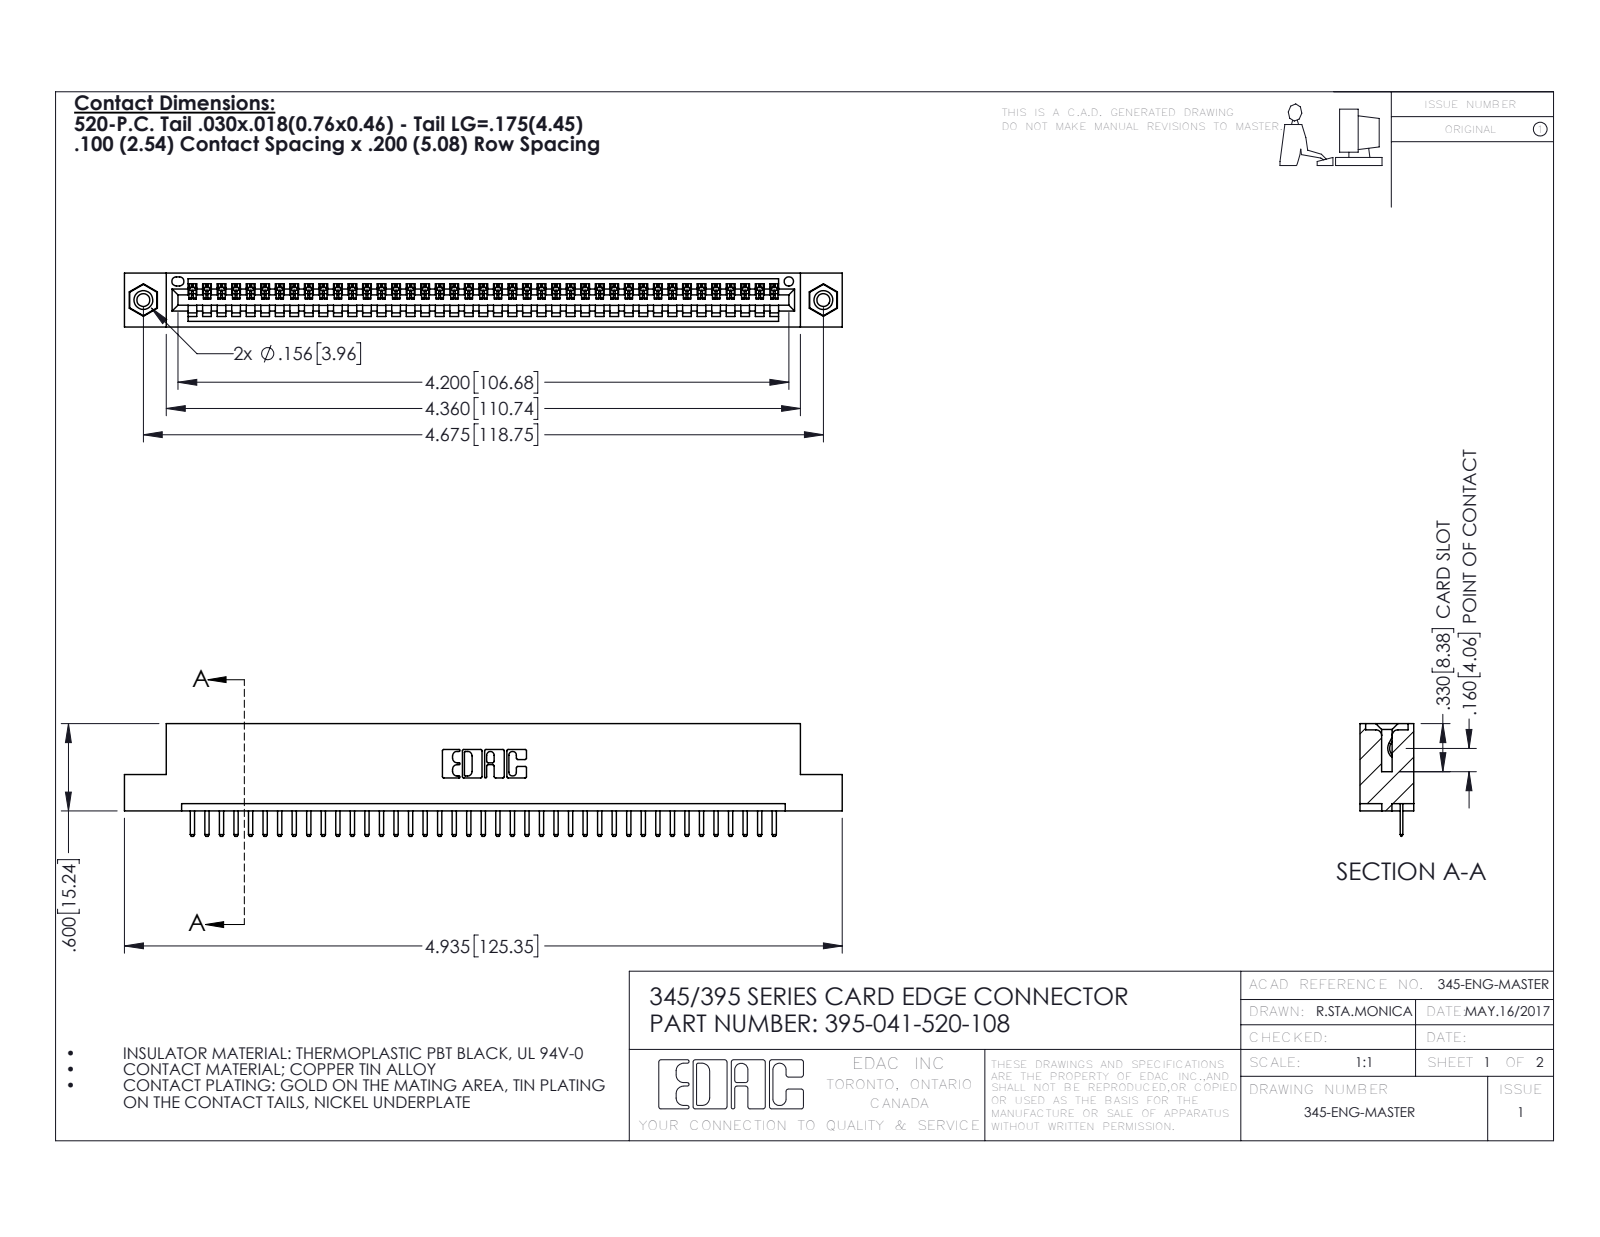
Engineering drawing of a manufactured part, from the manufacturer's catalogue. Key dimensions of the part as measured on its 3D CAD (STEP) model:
Part name (STEP PRODUCT): 345-250-001_345-250-003-102; 395-041-520-108; 345-292-001_345-293-120; 345 Part_Flush Mounting Lugs - 0.156 Dia-TI
STEP written by: SolidWorks 2016 (CONFIG_CONTROL_DESIGN)
Units: inches
Bodies: 44 solids, 2728 faces (1834 planar, 878 cylindrical, 16 other)
Overall size (bounding box): 4.935 × 0.775 × 0.37
Volume: 0.718 in³ · Surface area: 23.66 in²
Round holes (diameter × count): ⌀0.089 ×2, ⌀0.125 ×2, ⌀0.156 ×2, ⌀0.064 ×1
Round bosses / shafts (diameter × count): ⌀0.155 ×2
Partial cylindrical surfaces — rounded edges, fillets, slot ends (radius × count): R0.01 ×84, R0.006 ×82, R0.01 ×22, R0.007 ×6, R0.031 ×6, R0.026 ×3, R0.031 ×2, R0.04 ×2
Main face-to-face distances: 0.072, 0.298, 0.37, 0.2, 0.098, 0.272, 0.025, 0.225, 0.072, 0.149
Hole centre spacings: 0.27, 4.439, 4.675
